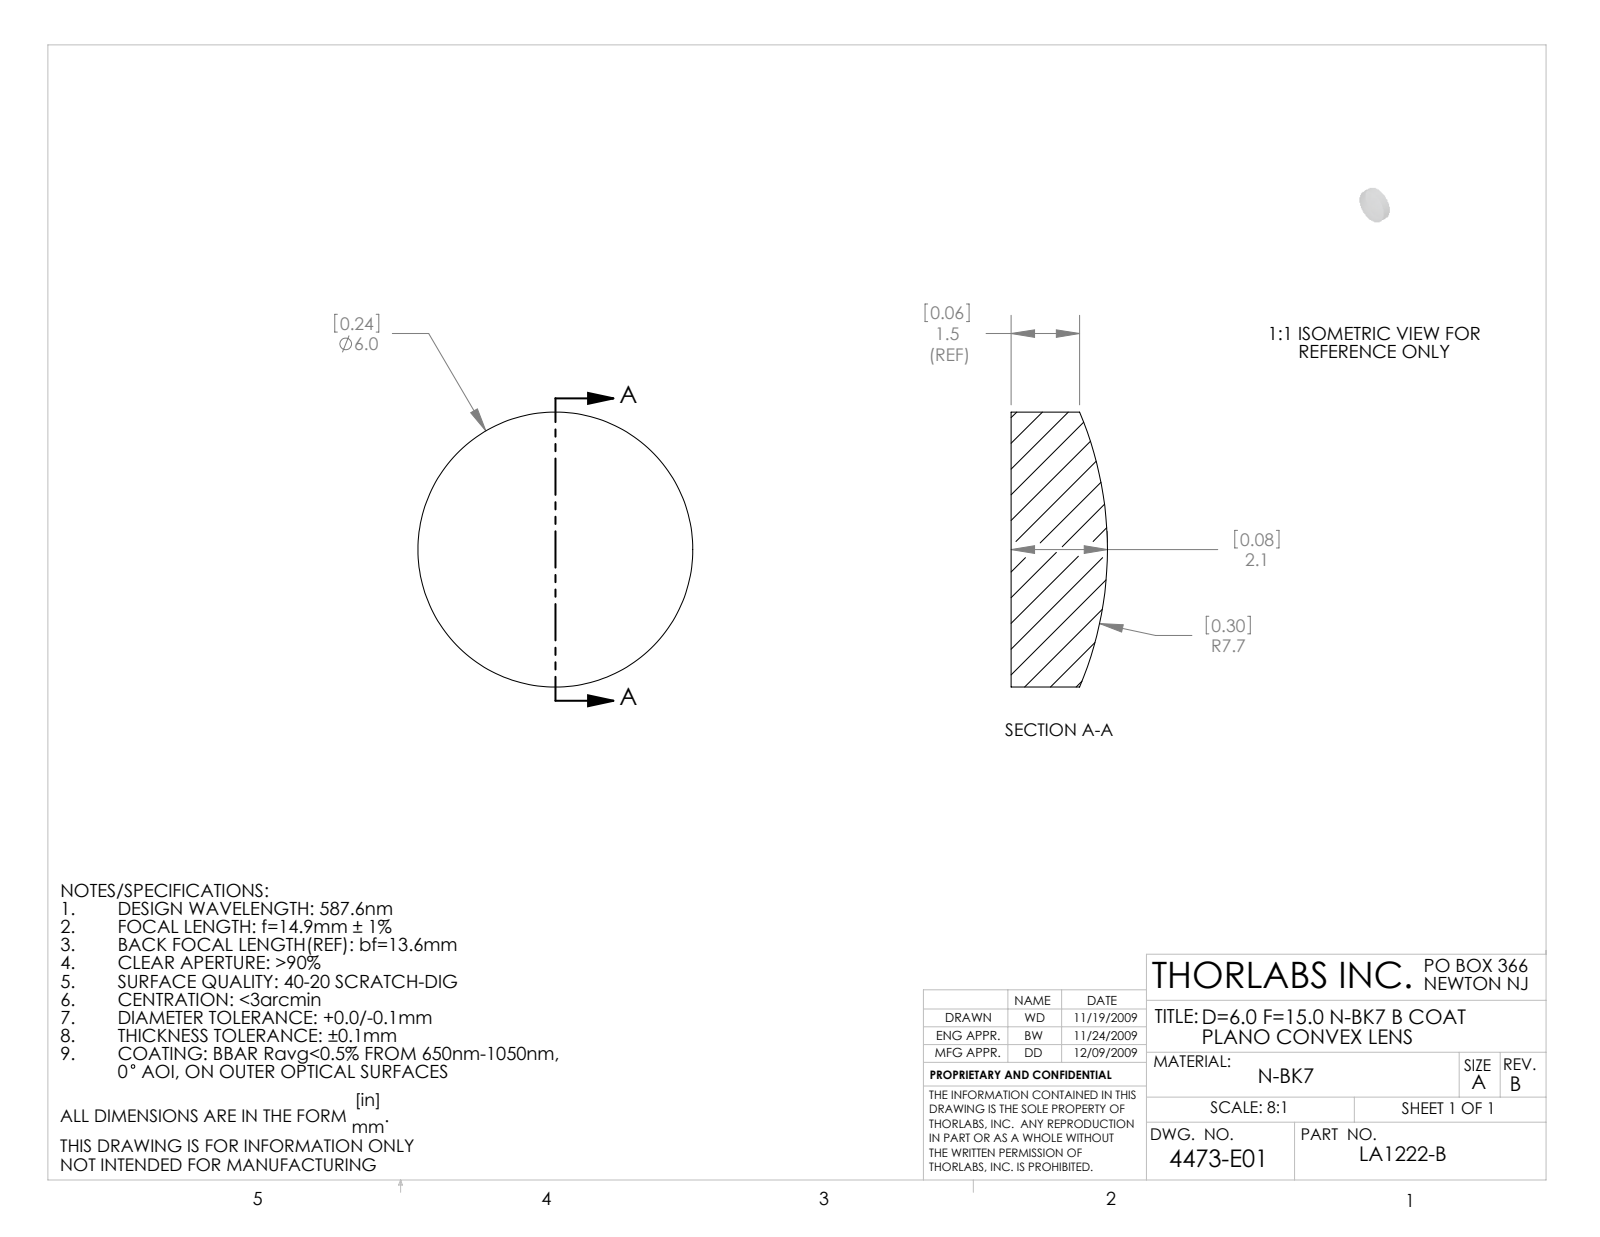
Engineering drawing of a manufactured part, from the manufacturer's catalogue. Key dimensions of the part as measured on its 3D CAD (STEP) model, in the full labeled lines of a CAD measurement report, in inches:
Part name (STEP PRODUCT): 4473-E0W
STEP written by: SolidWorks 2009 (AUTOMOTIVE_DESIGN)
Units: inches
Bodies: 1 solid, 5 faces (1 planar, 2 cylindrical, 2 other)
Overall size (bounding box): 0.236 × 0.236 × 0.083
Volume: 0.003 in³ · Surface area: 0.13 in²
Round bosses / shafts (diameter × count): ⌀0.236 ×1
